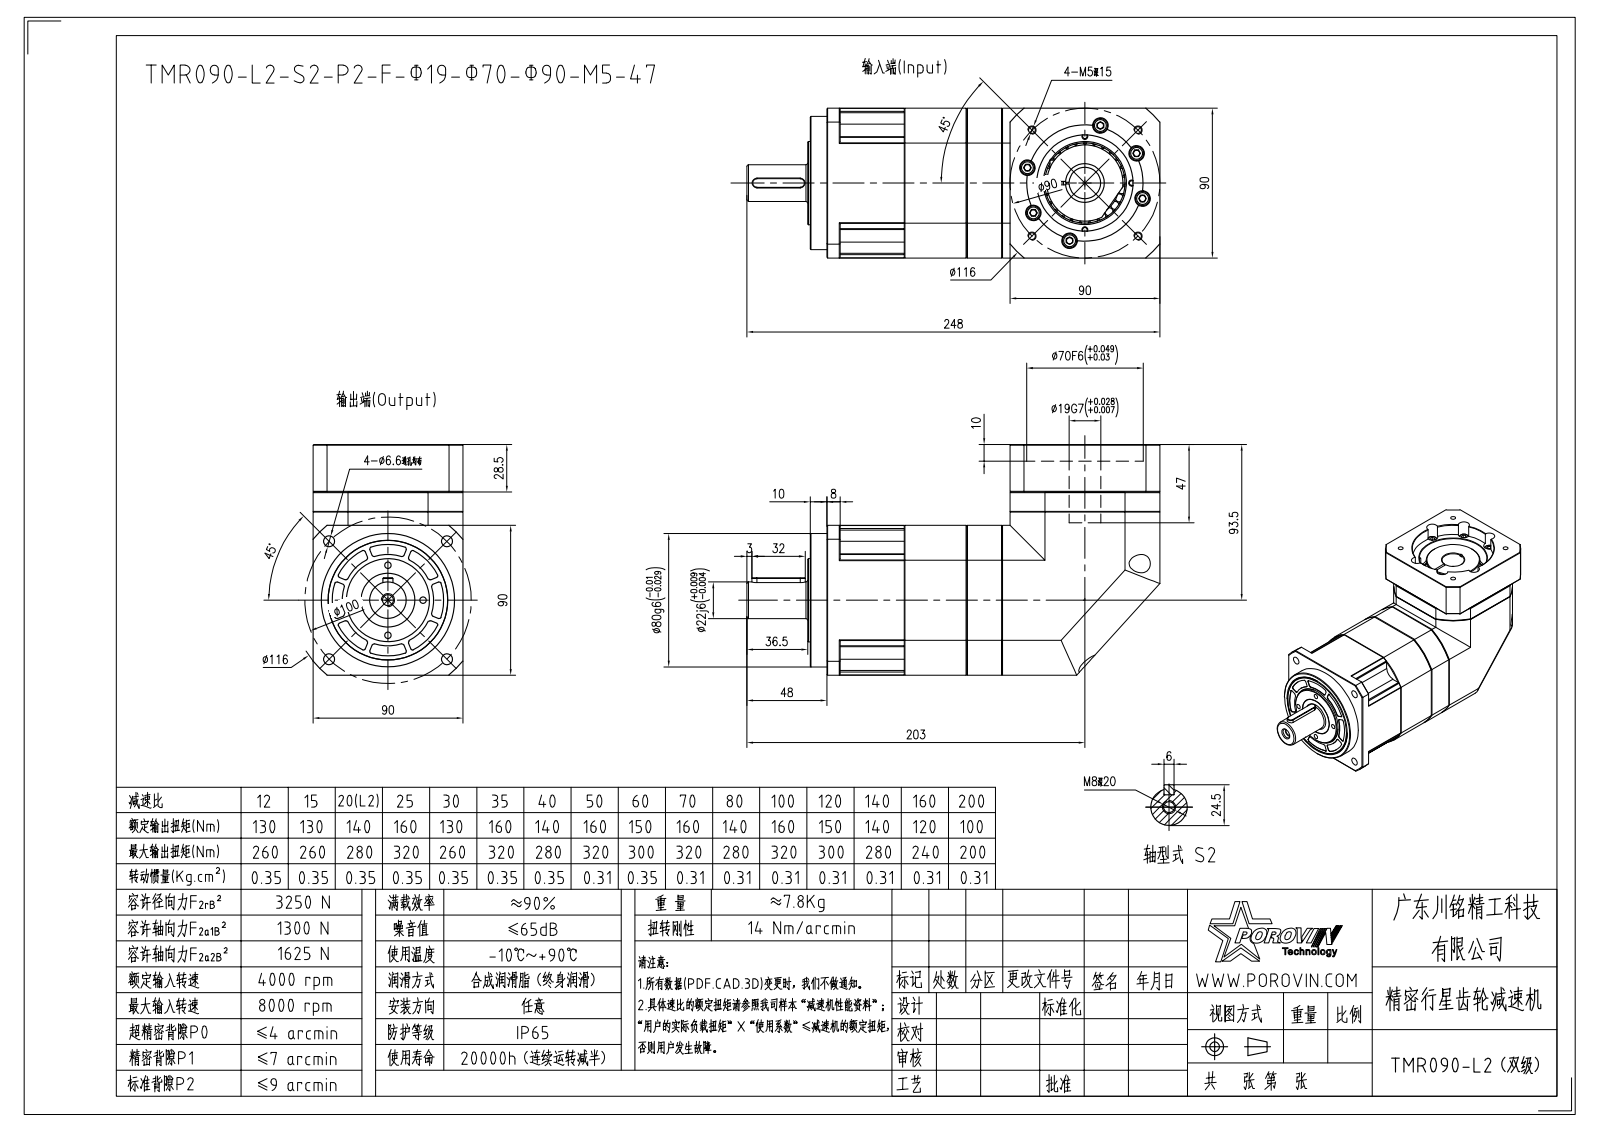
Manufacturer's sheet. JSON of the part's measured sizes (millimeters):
{"part_name": "M900001; HEXAGON_SOCKET_HEAD_CAP_SC-9564; SPRING_LOCK_WASHERS--NORM-19349; HEXAGON_SOCKET_HEAD_CAP_S-19443 (+8 more)", "step_written_by": "CREO PARAMETRIC BY PTC INC, 2020053 (CONFIG_CONTROL_DESIGN)", "units": "millimeters", "bodies": {"solids": 43, "faces": 1321, "planar": 526, "cylindrical": 561, "other": 234}, "overall_size": [248, 138.5, 90], "volume_mm3": 1611000, "surface_area_mm2": 238403, "round_holes": [[5.4, 12], [5.5, 12], [9.5, 12], [4.2, 11], [6.6, 10], [6.5, 5], [4, 4], [6.68, 4], [11, 4], [5, 1], [6.8, 1], [8.4, 1]], "round_bosses_or_shafts": [[8.5, 12], [8, 12], [5, 12], [10, 4], [9.88, 4], [6, 4], [80, 1], [78, 1]], "partial_cylinders_radius": [[1, 92], [7.5, 4], [51, 3], [3, 2], [58, 2], [4, 1], [5.25, 1], [20.75, 1]], "face_to_face_distances": [90, 12, 21.5, 21.3, 37.5, 58.8, 59, 110, 10, 26], "hole_center_spacings": [35.75, 27.36, 38.16, 44, 66.06, 66.53, 64.31, 80.07]}
